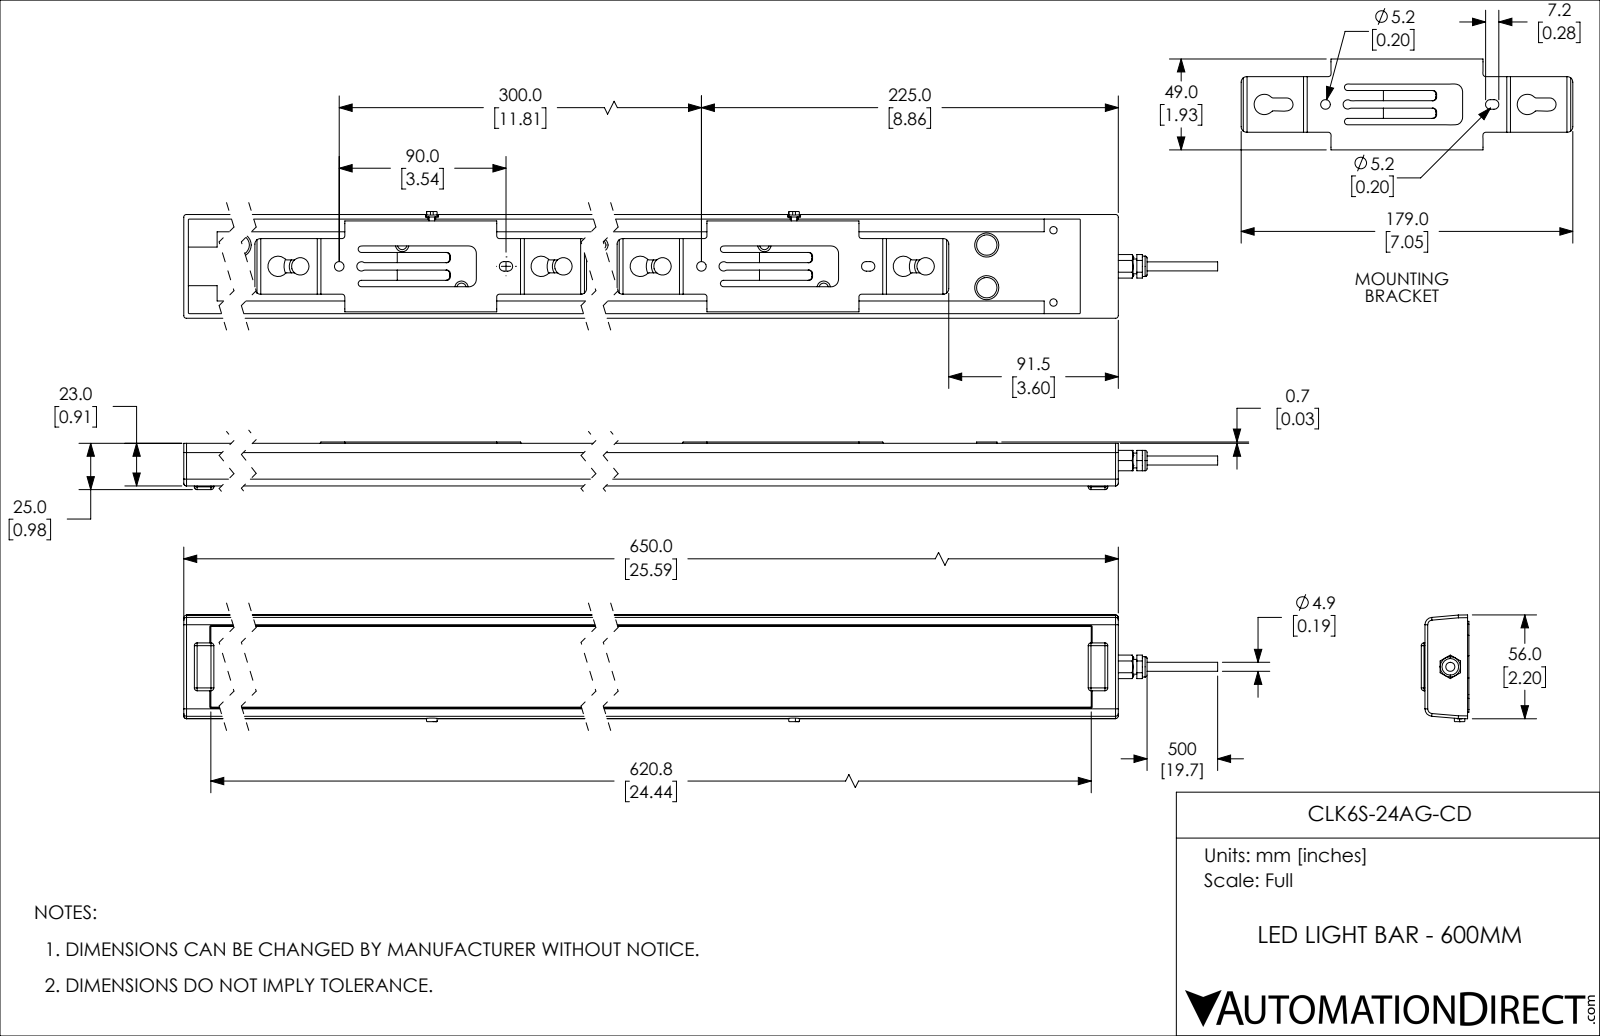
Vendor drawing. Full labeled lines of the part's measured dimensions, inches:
Part name (STEP PRODUCT): CLK6S-24AG-CD
STEP written by: SolidWorks 2018 (AUTOMOTIVE_DESIGN)
Units: inches
Bodies: 5 solids, 394 faces (180 planar, 104 cylindrical, 110 other)
Overall size (bounding box): 27.701 × 2.268 × 1.012
Volume: 36.28 in³ · Surface area: 270.3 in²
Round holes (diameter × count): ⌀0.157 ×4, ⌀0.118 ×2, ⌀0.205 ×2
Round bosses / shafts (diameter × count): ⌀0.433 ×7, ⌀0.512 ×6, ⌀0.37 ×4, ⌀0.256 ×4, ⌀0.315 ×1, ⌀0.193 ×1
Partial cylindrical surfaces — rounded edges, fillets, slot ends (radius × count): R0.059 ×20, R0.079 ×8, R0.102 ×4, R0.157 ×2
Main face-to-face distances: 0.697, 0.059, 0.269, 1.739, 2.008, 0.404, 0.293, 0.236, 0.64, 0.933
Hole centre spacings: 1.535, 3.626, 7.52, 11.811, 15.374, 19.307, 22.835, 22.886
